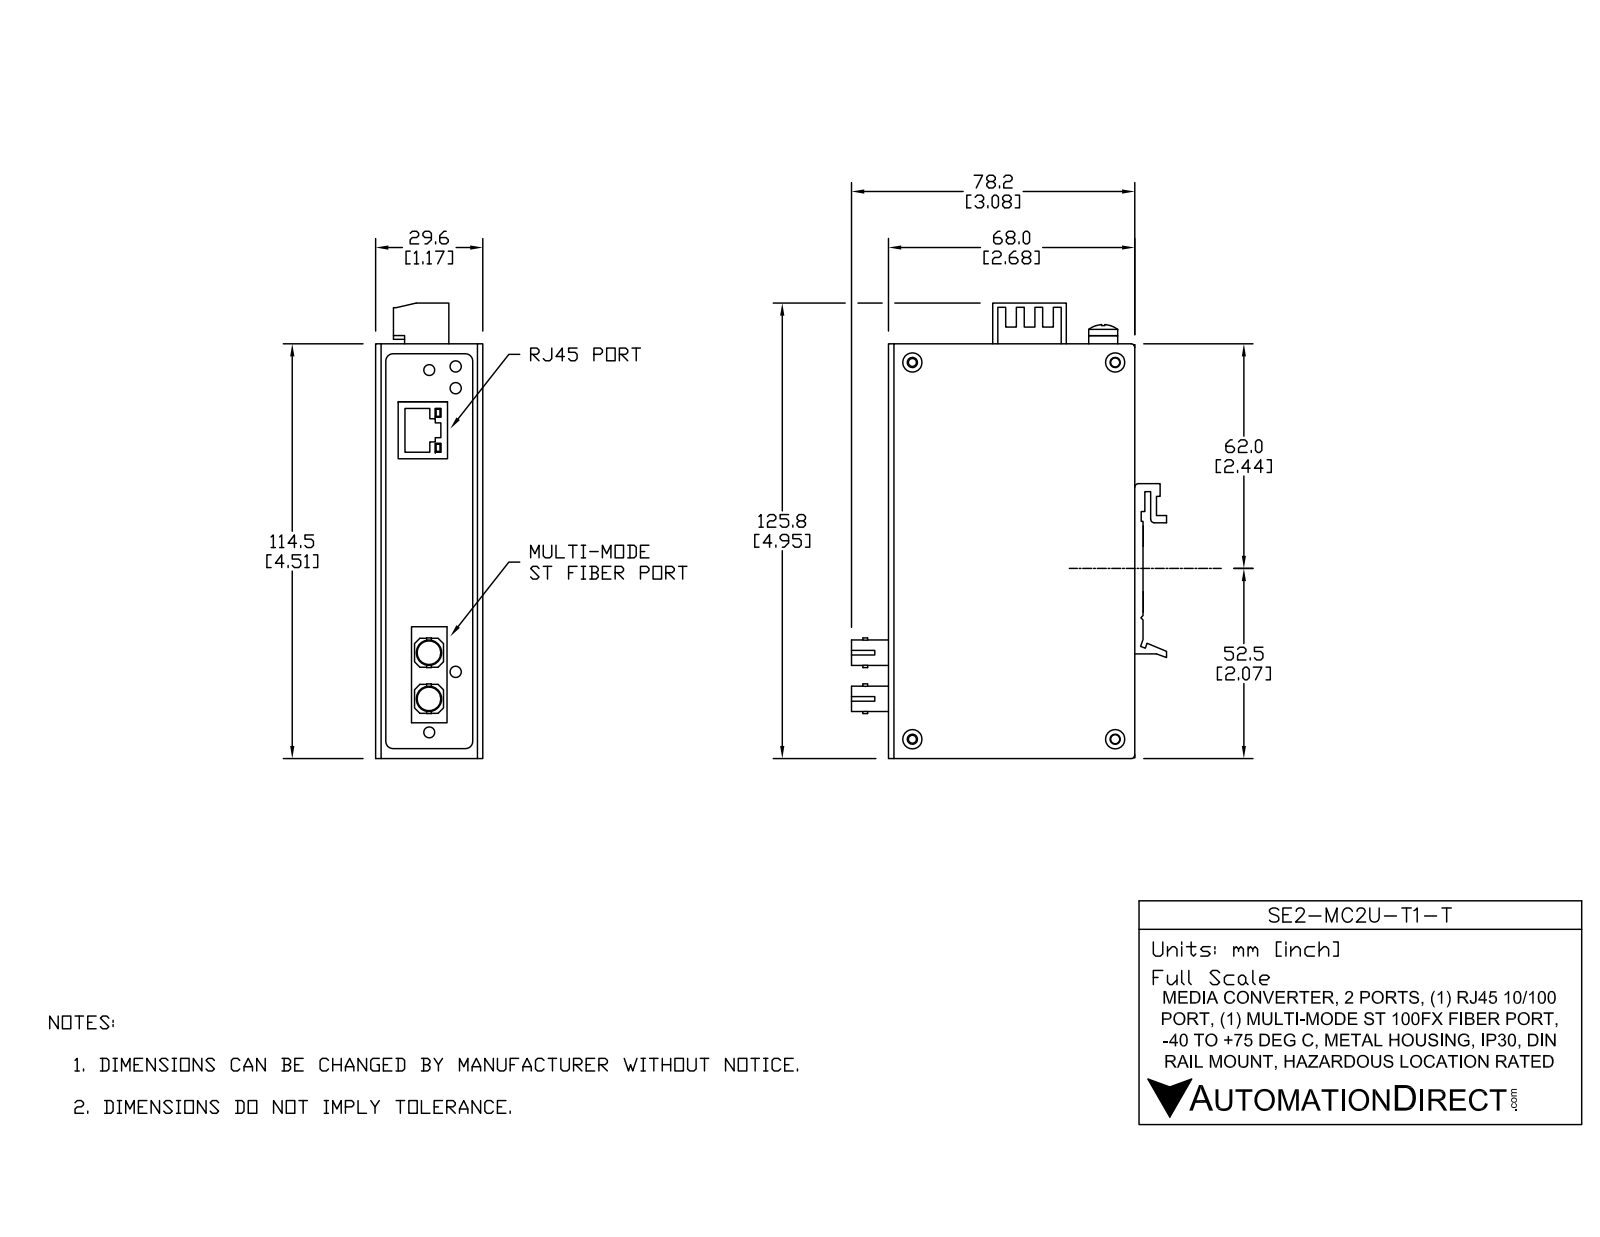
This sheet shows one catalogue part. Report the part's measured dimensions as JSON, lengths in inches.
{"part_name": "SE2-MC2U-T1-T", "step_written_by": "SolidWorks 2017 (AUTOMOTIVE_DESIGN)", "units": "inches", "bodies": {"solids": 10, "faces": 798, "planar": 521, "cylindrical": 230, "other": 47}, "overall_size": [4.951, 3.425, 1.165], "volume_in3": 2.716, "surface_area_in2": 125.8, "round_holes": [[0.11, 4], [0.15, 4], [0.122, 3], [0.118, 2], [0.134, 2], [0.256, 2], [0.155, 1]], "round_bosses_or_shafts": [[0.142, 4], [0.276, 2], [0.217, 2], [0.197, 2], [0.118, 2], [0.315, 1], [0.157, 1], [0.051, 1]], "partial_cylinders_radius": [[0.024, 96], [0.026, 16], [0.079, 8], [0.118, 8], [0.008, 6], [0.041, 6], [0.039, 5], [0.012, 4]], "face_to_face_distances": [0.039, 0.02, 1.087, 1.126, 0.079, 1.106, 1.067, 1.047, 0.059, 2.618], "hole_center_spacings": [0.203, 0.4, 2.205, 4.094, 4.65, 0.197, 0.236, 0.29]}
